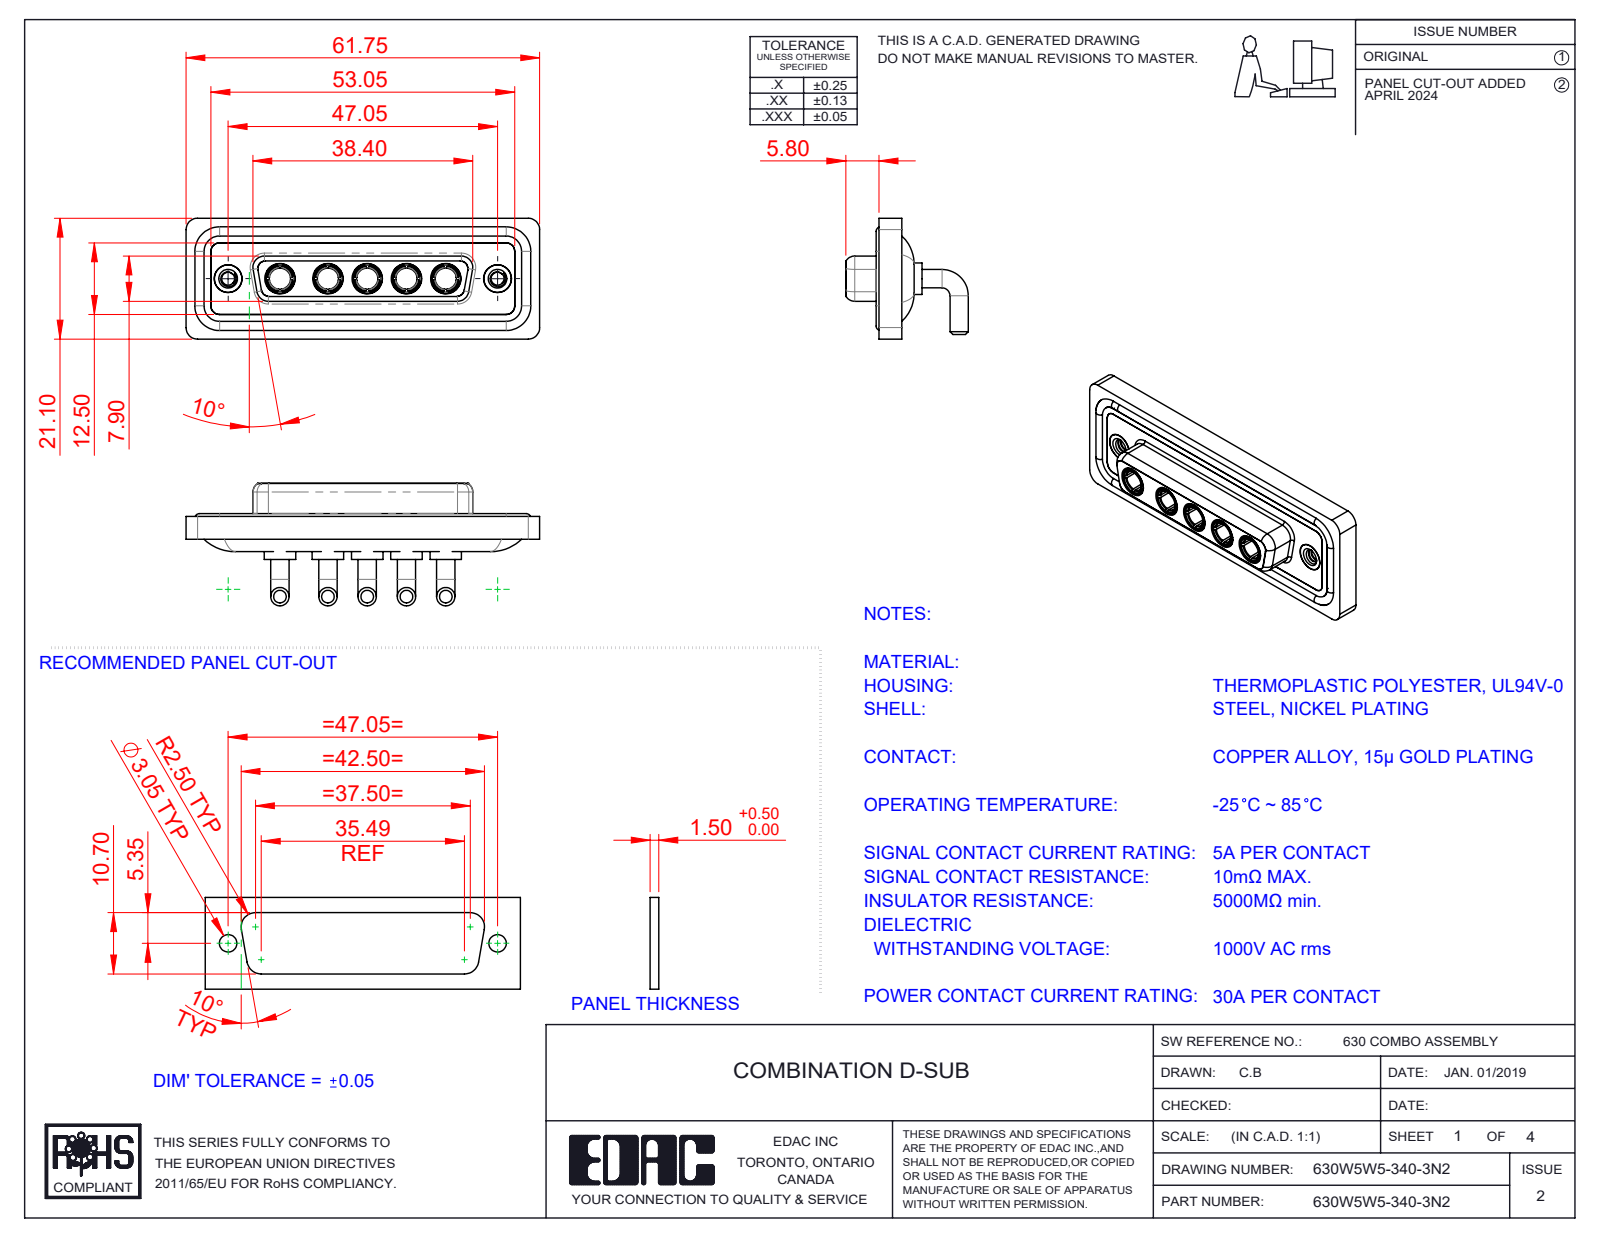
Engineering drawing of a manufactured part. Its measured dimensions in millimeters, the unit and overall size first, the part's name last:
Units: millimetres
Overall size (bounding box): 61.75 × 21.4 × 21.1
Round holes (diameter × count): ⌀4.85 ×7, ⌀3.7 ×5, ⌀5.3 ×5, ⌀2.26 ×2, ⌀4 ×2, ⌀4.05 ×2, ⌀5 ×2
Round bosses / shafts (diameter × count): ⌀3.2 ×10, ⌀5.5 ×5, ⌀5.2 ×5, ⌀4.96 ×5, ⌀4.75 ×5, ⌀3.75 ×5, ⌀1.6 ×4, ⌀4.95 ×2
Partial cylindrical surfaces — rounded edges, fillets, slot ends (radius × count): R1.5 ×18, R2 ×18, R1.35 ×8, R1.6 ×8, R2.1 ×5, R0.25 ×4, R0.5 ×4, R0.6 ×4
Main face-to-face distances: 0.4, 1.8, 4.1, 1.1, 1.5, 2.5, 3.1, 3.7, 1.6, 2.9
Hole centre spacings: 6.86, 9.04, 38.01, 6.87, 8.38, 13.72, 13.73, 15.25
Volume: 8 575 mm³ · Surface area: 13 905 mm²
Bodies: 17 solids, 776 faces (250 planar, 313 cylindrical, 213 other)
Part name (STEP PRODUCT): 630Combo Shell Rear_25 Contacts; 630Combo Waterproof Housing_25 Contacts; 630W5W5-340-3N2; 630Combo Threaded Rivet_2 (+3 more)
STEP written by: SolidWorks 2023 (CONFIG_CONTROL_DESIGN)
